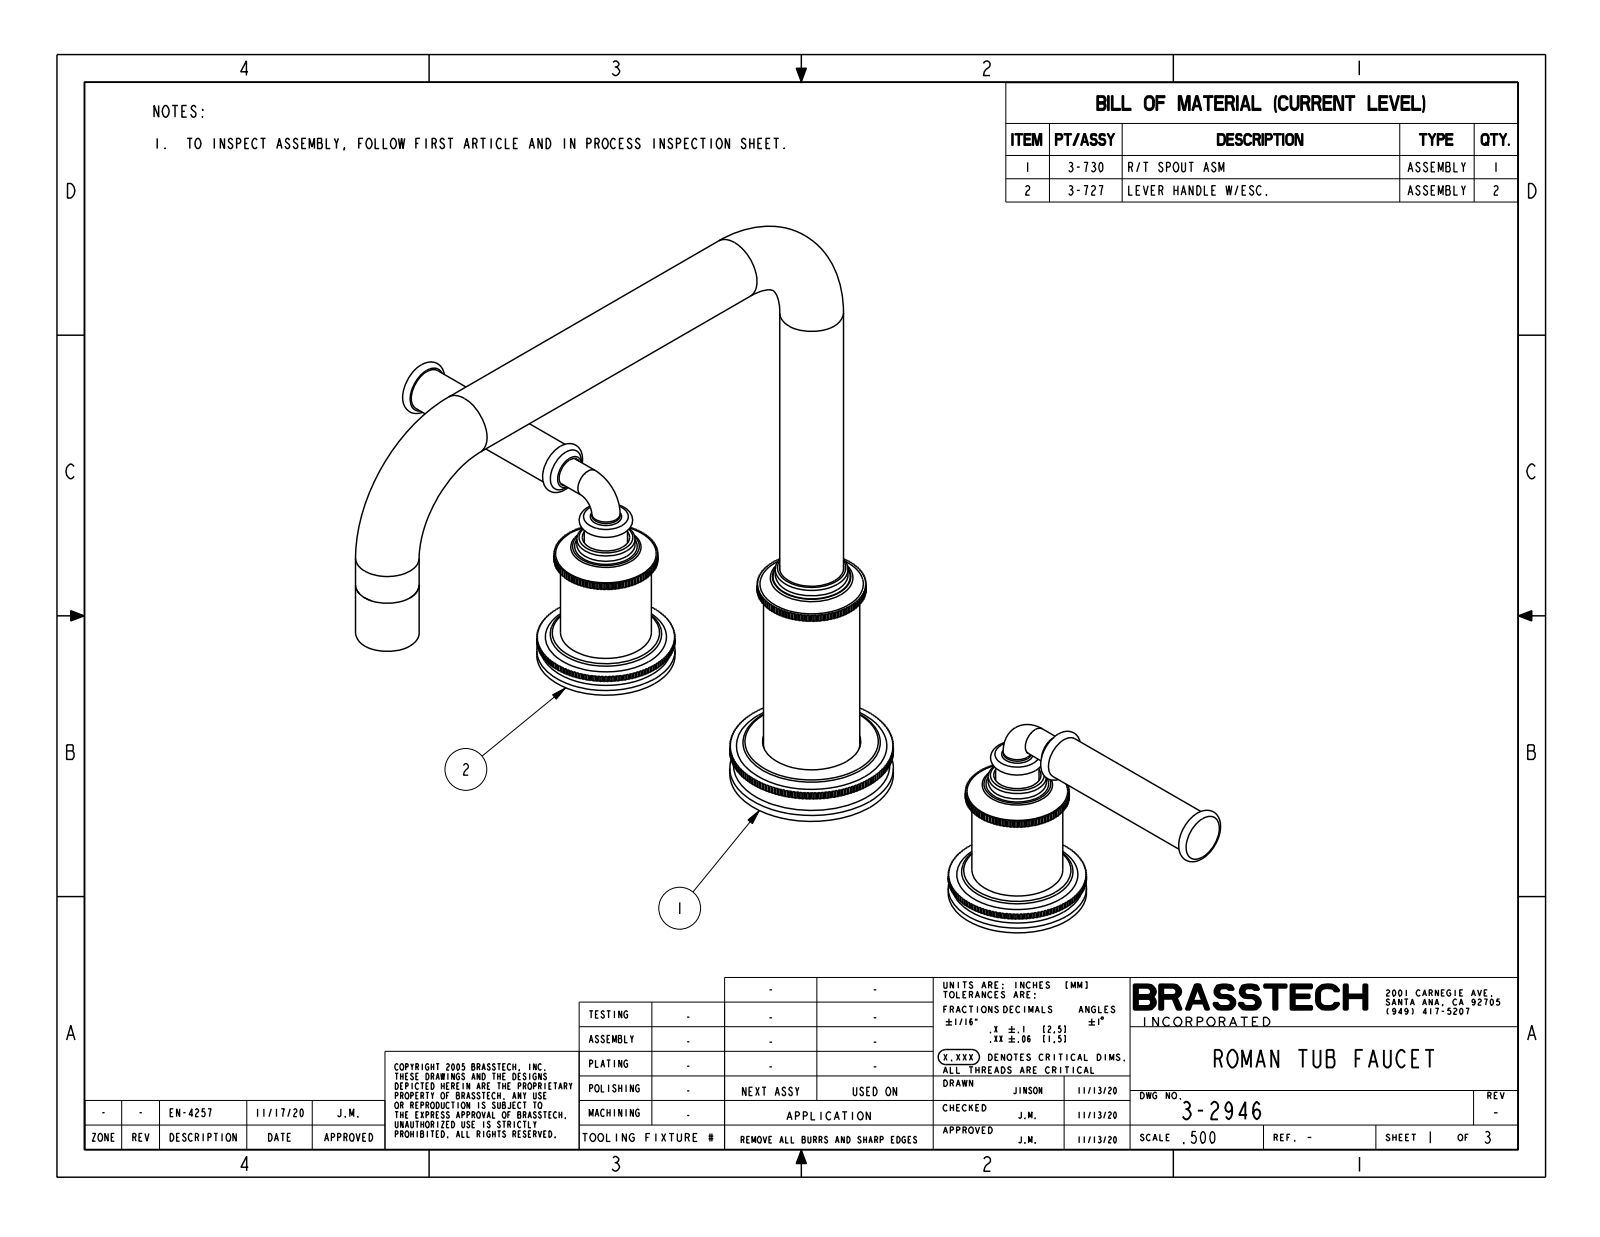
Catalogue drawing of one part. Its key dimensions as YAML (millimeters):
part_name: "3-2946"
step_written_by: "CREO PARAMETRIC BY PTC INC, 2019352 (CONFIG_CONTROL_DESIGN)"
units: millimeters
bodies: {solids: 3, faces: 2154, planar: 1362, cylindrical: 718, other: 74}
overall_size: [386.3, 249.2, 246.3]
volume: 378200
surface_area: 73100
round_holes:
  - {diameter: 10.4, count: 1}
  - {diameter: 17.6, count: 1}
round_bosses_or_shafts:
  - {diameter: 22.2, count: 3}
  - {diameter: 9.9, count: 3}
  - {diameter: 48.3, count: 2}
  - {diameter: 45.7, count: 2}
  - {diameter: 31.8, count: 2}
  - {diameter: 30.5, count: 2}
  - {diameter: 20.3, count: 2}
  - {diameter: 15.1, count: 2}
partial_cylinders:
  - {radius: 18.2, count: 2}
  - {radius: 19.1, count: 1}
face_to_face_distances: [14, 7.9, 6.1, 9.7, 1.8, 4.3, 40.9, 33, 31.2, 26.9]
